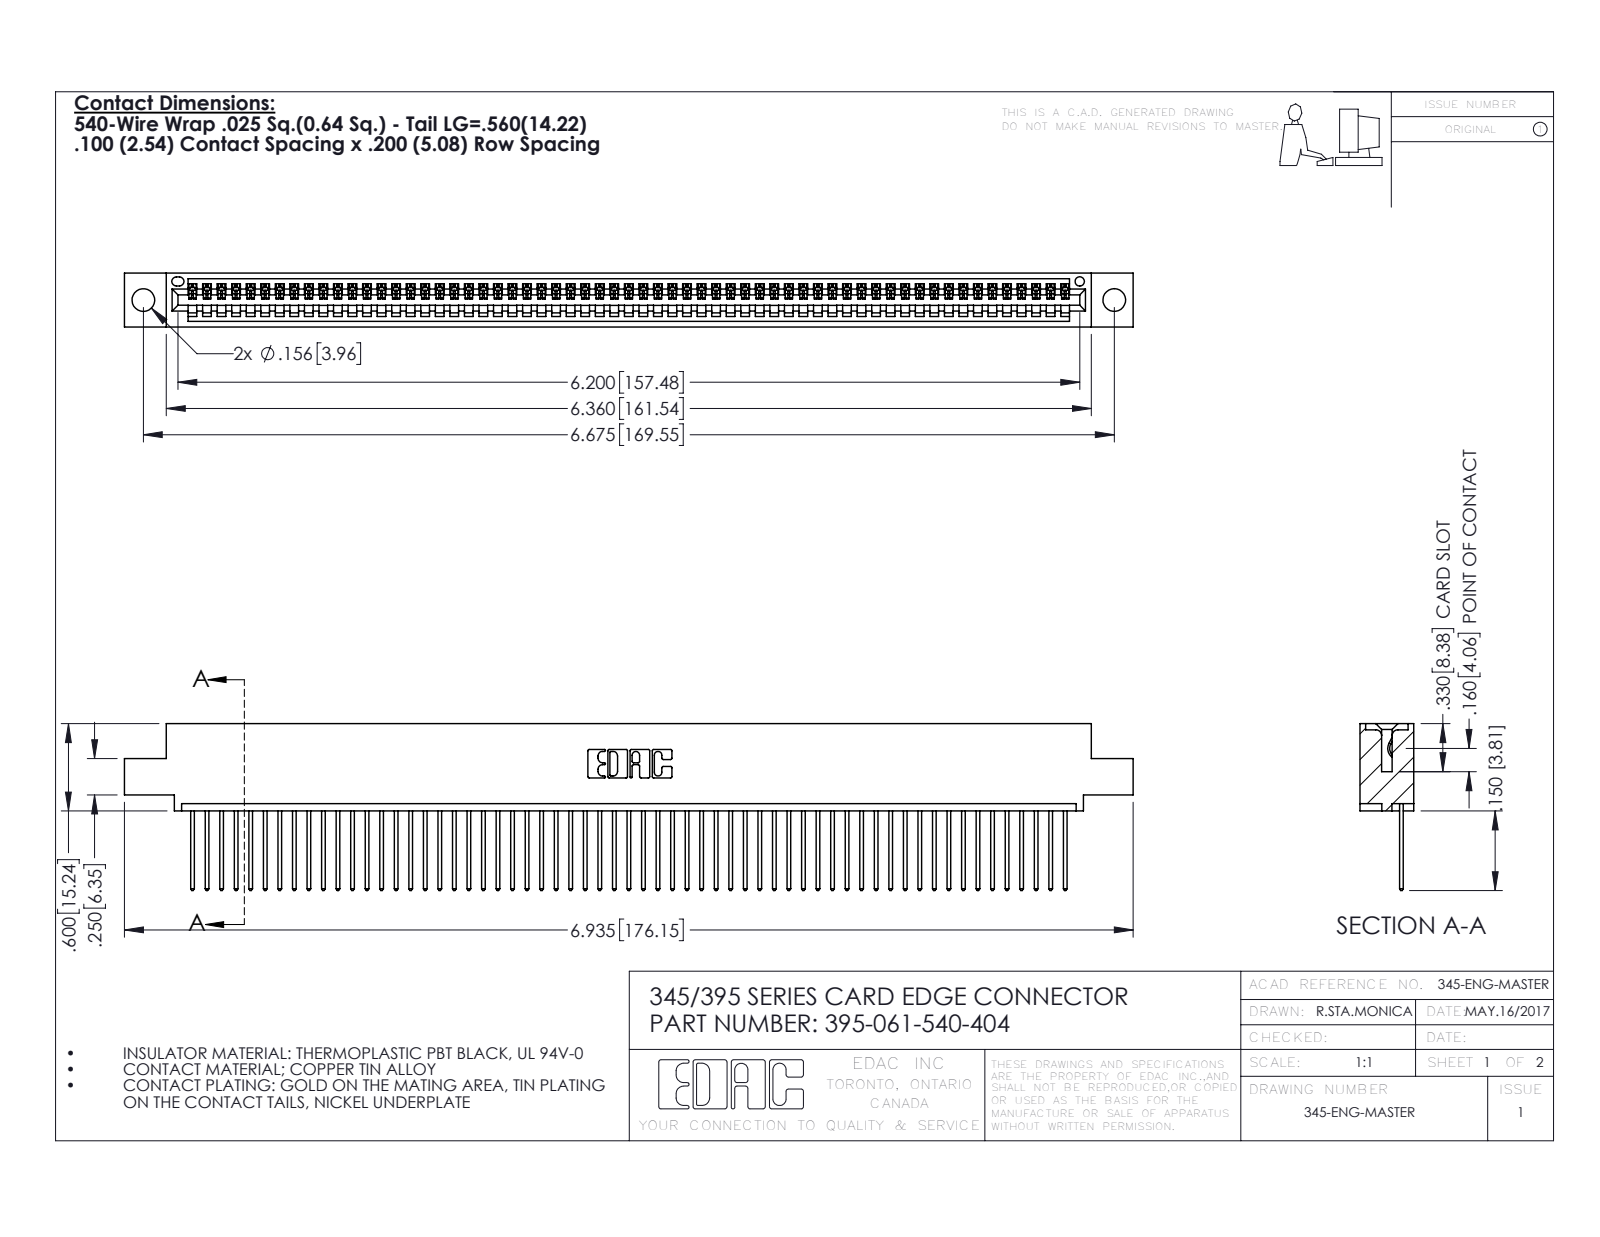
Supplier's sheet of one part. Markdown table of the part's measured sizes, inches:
| quantity | value |
| --- | --- |
| part name | 345 Part_0.110 Offset - 0.156 Dia-TH; 395-061-540-404; 345-292-001_345-293-140 |
| STEP written by | SolidWorks 2016 (CONFIG_CONTROL_DESIGN) |
| units | inches |
| bodies | 62 solids, 3668 faces (2524 planar, 1144 cylindrical, 0 other) |
| overall size | 6.935 × 1.147 × 0.37 |
| volume | 1.026 in³ |
| surface area | 35.77 in² |
| round holes (diameter × count) | 0.156 × 2, 0.064 × 1 |
| partial cylindrical surfaces (radius × count) | 0.006 × 122, 0.01 × 122, 0.01 × 22, 0.007 × 6, 0.031 × 6, 0.026 × 3, 0.031 × 2, 0.04 × 2 |
| main face-to-face distances | 0.298, 0.072, 0.37, 0.098, 0.272, 0.025, 0.2, 0.225, 0.149, 0.072 |
| hole center spacings | 0.27, 6.439, 6.675 |
